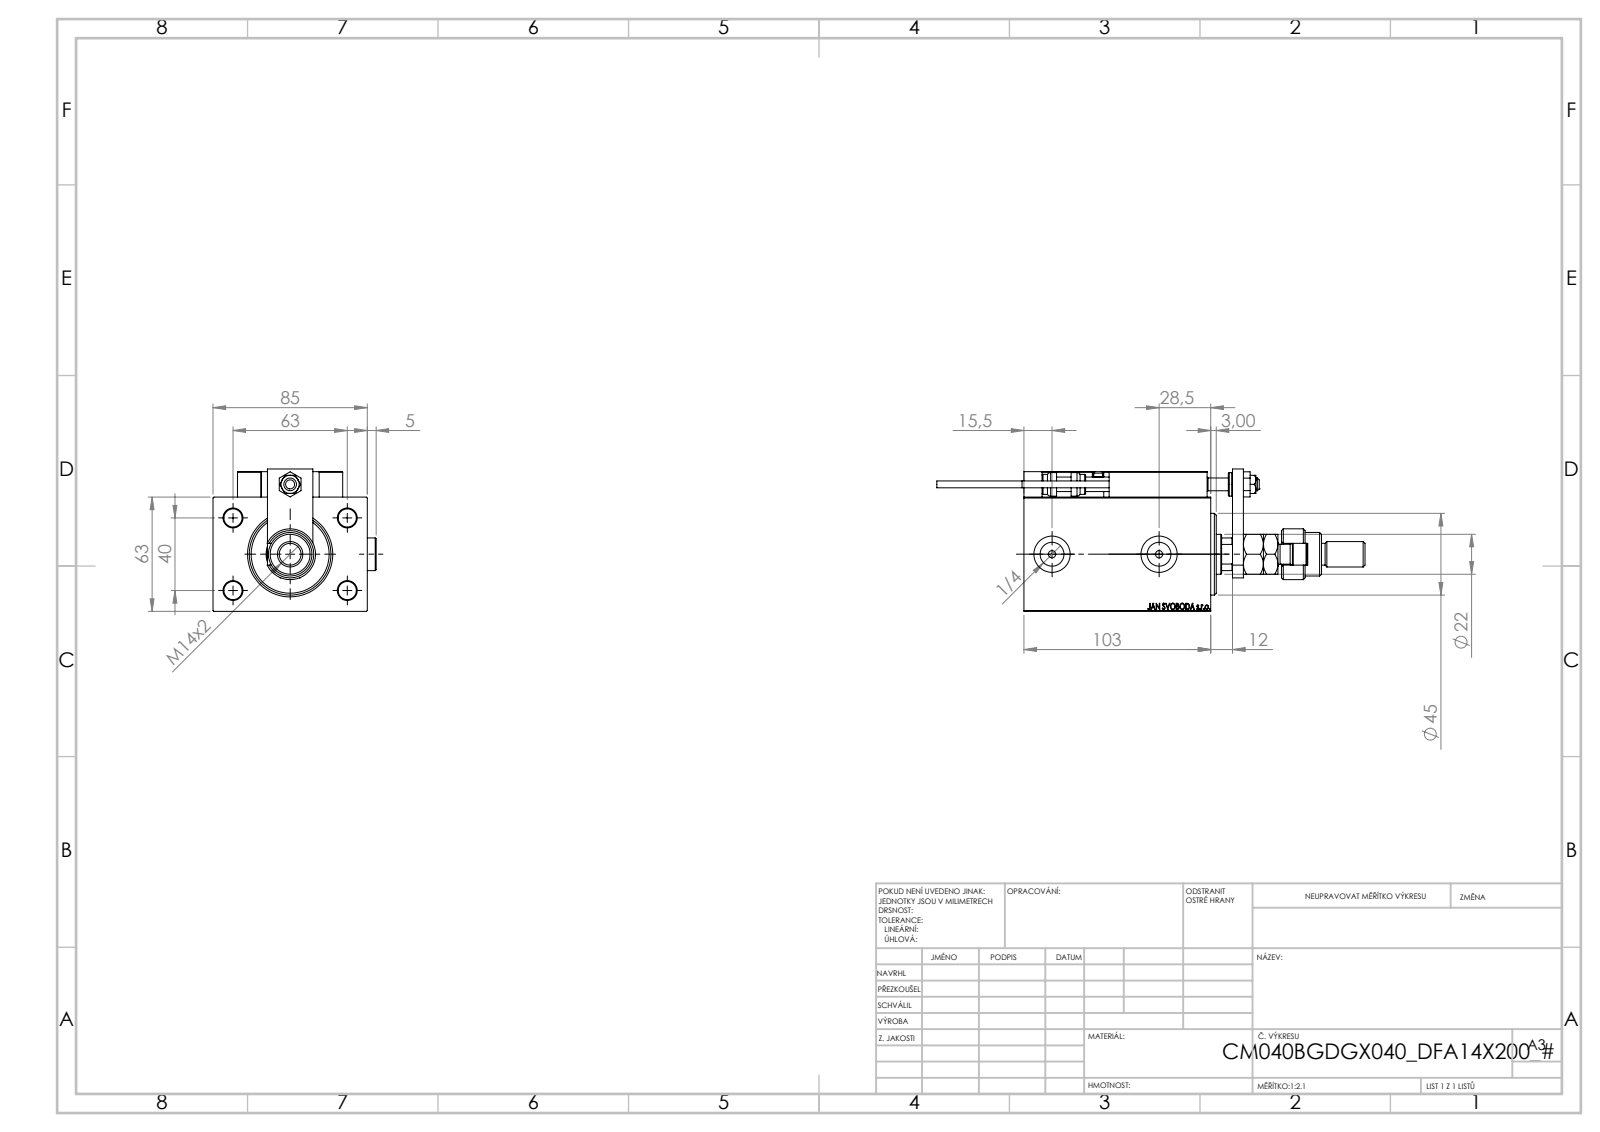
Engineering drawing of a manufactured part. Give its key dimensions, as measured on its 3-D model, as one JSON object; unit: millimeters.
{"part_name": "ALLEN BOLT D8; X_Y_DFA; MFA; Zatka_OIL_PORT (+7 more)", "step_written_by": "SolidWorks 2019 (CONFIG_CONTROL_DESIGN)", "units": "millimeters", "bodies": {"solids": 28, "faces": 1457, "planar": 623, "cylindrical": 213, "other": 621}, "overall_size": [236, 89.9, 78.5], "volume_mm3": 574253, "surface_area_mm2": 113234, "round_holes": [[4, 6], [8, 5], [3.2, 4], [10, 4], [5, 2], [13.16, 2], [20, 2], [7, 1], [12.5, 1], [16.5, 1], [22, 1], [25.5, 1]], "round_bosses_or_shafts": [[18, 3], [11, 2], [5, 2], [3.8, 2], [28, 1], [24, 1], [14, 1], [13, 1]], "partial_cylinders_radius": [[0.3, 30], [3, 2], [9.75, 1], [10.5, 1]], "face_to_face_distances": [63, 12, 85, 91, 103, 14, 30, 18, 77, 15], "hole_center_spacings": [37.31, 11.37, 20, 29.59, 29.69, 36.06, 36.53, 40]}
